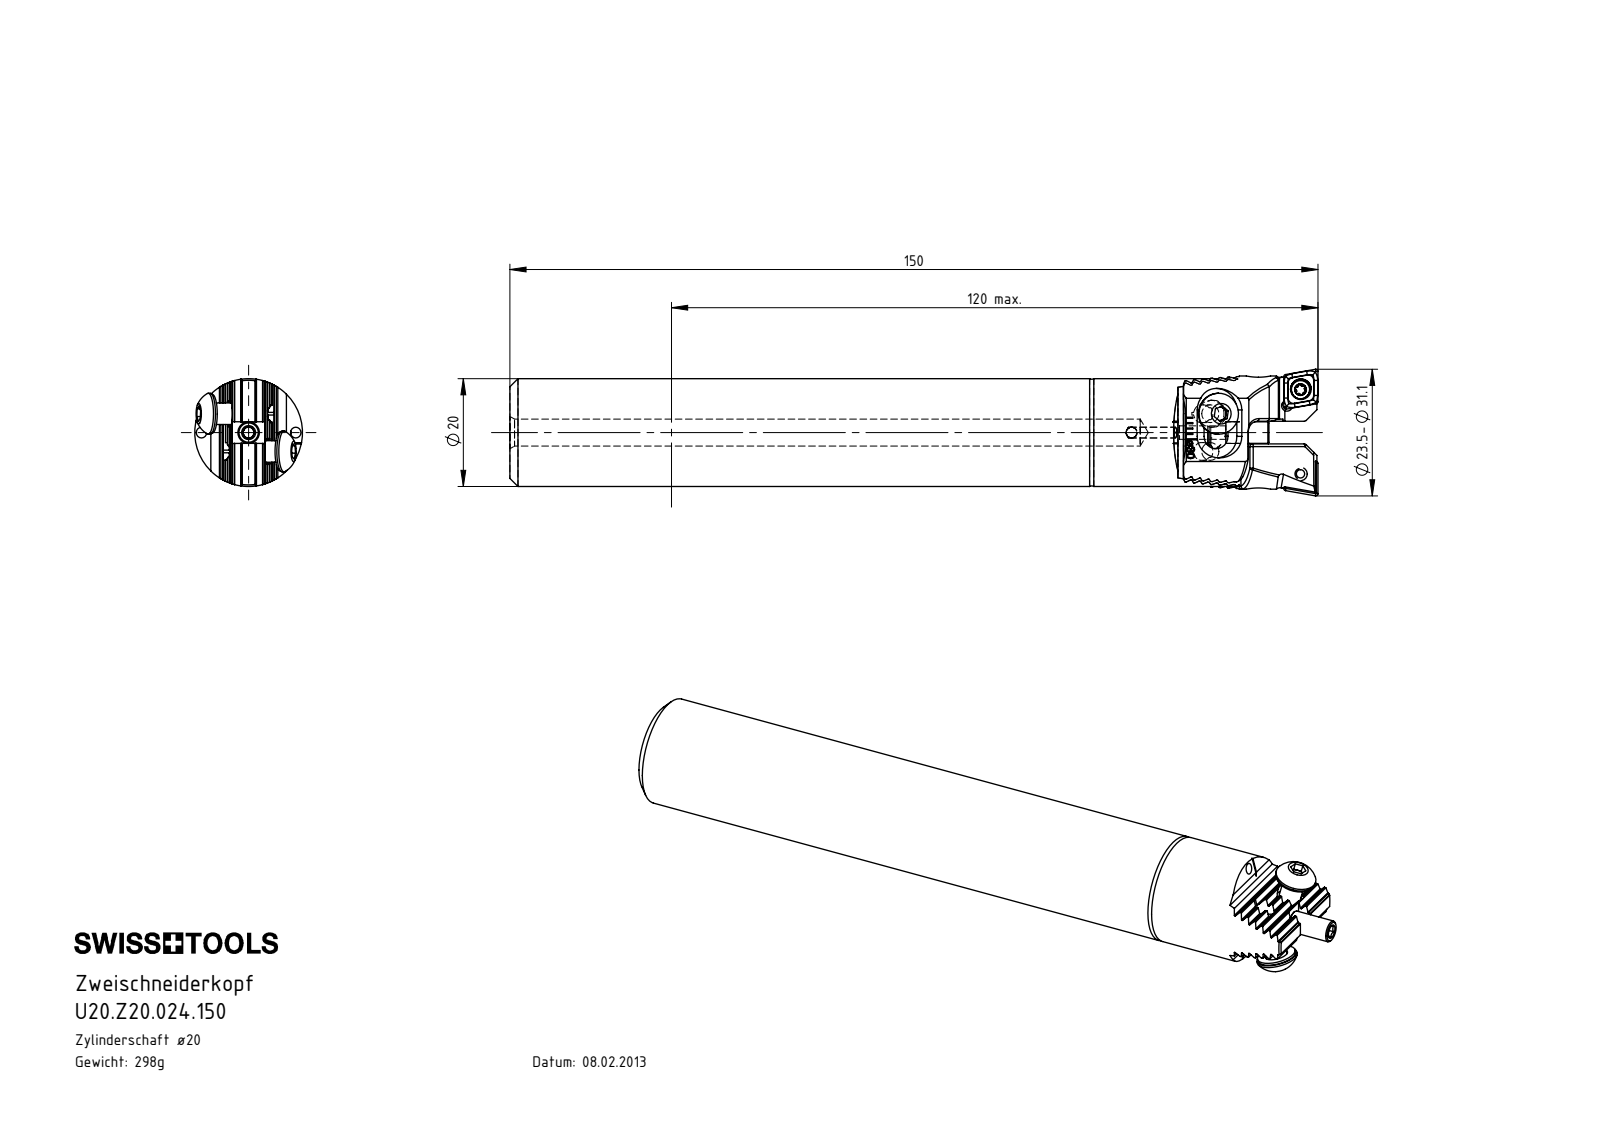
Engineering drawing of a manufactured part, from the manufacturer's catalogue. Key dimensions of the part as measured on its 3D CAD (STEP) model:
Part name (STEP PRODUCT): Z20-ER1.001.008; Z20-ER1.003.008_A_gespannt; Z20-ER1.002.008_A; Z20-ER2.001.013_A (+2 more)
STEP written by: SolidWorks 2017 (AUTOMOTIVE_DESIGN)
Units: millimetres
Bodies: 6 solids, 239 faces (149 planar, 62 cylindrical, 28 other)
Overall size (bounding box): 140.9 × 20 × 20
Volume: 38 212 mm³ · Surface area: 12 003 mm²
Round holes (diameter × count): ⌀2 ×4, ⌀5 ×3, ⌀3.3 ×2, ⌀4.3 ×2, ⌀2.5 ×1
Round bosses / shafts (diameter × count): ⌀4 ×3, ⌀7.6 ×2, ⌀7.2 ×2, ⌀20 ×1, ⌀3 ×1, ⌀2.2 ×1
Partial cylindrical surfaces — rounded edges, fillets, slot ends (radius × count): R0.12 ×14, R220 ×2
Main face-to-face distances: 1.43, 4.28, 5.71, 2.86, 2.85, 7.14, 1.42, 0.4, 124, 3.6
